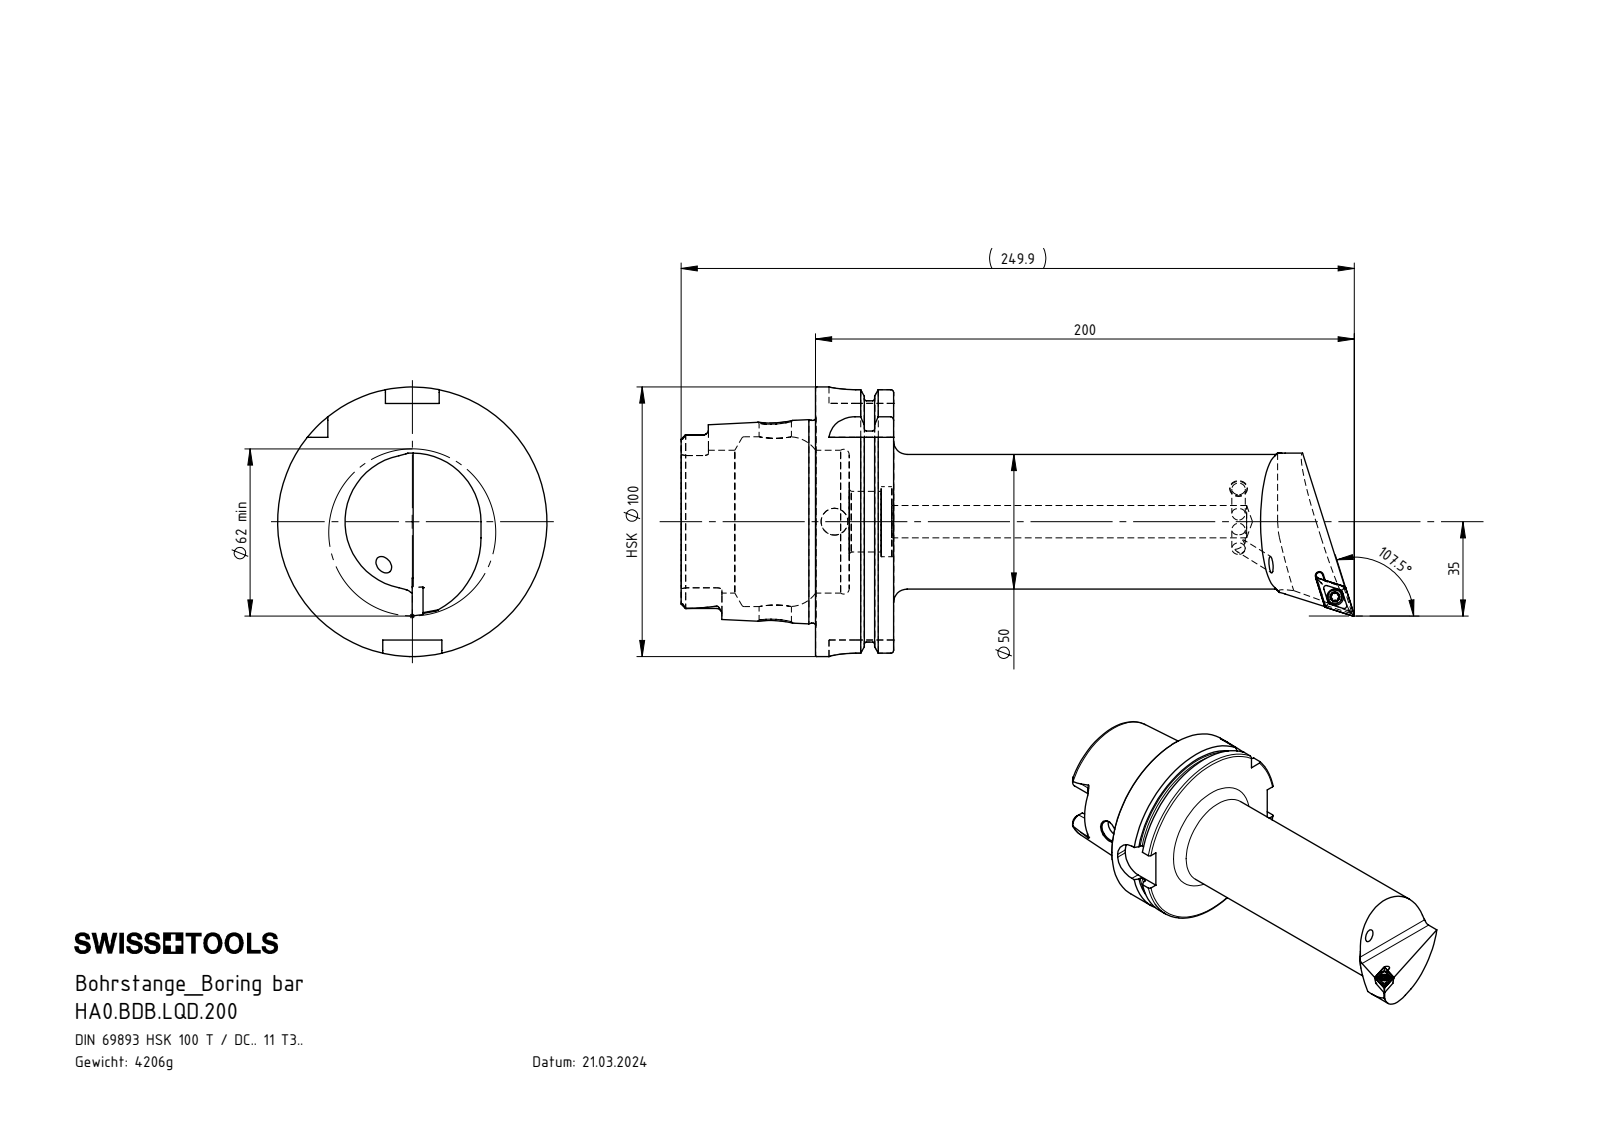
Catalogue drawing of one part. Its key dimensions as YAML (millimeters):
part_name: "DCMT11T304; WCB-ER2.001.009_A; ISO 4026 - M5 x 8; HA0.BDB.LQD.200 (+1 more)"
step_written_by: "SolidWorks 2022 (AUTOMOTIVE_DESIGN)"
units: millimeters
bodies: {solids: 4, faces: 288, planar: 81, cylindrical: 87, other: 120}
overall_size: [249.91, 100, 100]
volume: 533766
surface_area: 80496
round_holes:
  - {diameter: 5, count: 2}
  - {diameter: 12, count: 2}
  - {diameter: 3.3, count: 1}
  - {diameter: 4.4, count: 1}
  - {diameter: 6.1, count: 1}
  - {diameter: 6.5, count: 1}
  - {diameter: 10, count: 1}
  - {diameter: 22.5, count: 1}
  - {diameter: 26, count: 1}
  - {diameter: 53, count: 1}
  - {diameter: 63, count: 1}
round_bosses_or_shafts:
  - {diameter: 100, count: 1}
  - {diameter: 91.95, count: 1}
  - {diameter: 75.26, count: 1}
  - {diameter: 50, count: 1}
  - {diameter: 5.25, count: 1}
  - {diameter: 4, count: 1}
partial_cylinders:
  - {radius: 0.34, count: 6}
  - {radius: 0.59, count: 6}
  - {radius: 1.9, count: 6}
  - {radius: 10, count: 4}
  - {radius: 4.83, count: 2}
  - {radius: 4.88, count: 2}
  - {radius: 1.25, count: 1}
  - {radius: 3, count: 1}
face_to_face_distances: [28.95, 16.5, 12.45, 49.9, 62.35, 78.85, 87.8, 78.2, 28.3, 15.85]
hole_center_spacings: [187.9, 188]
